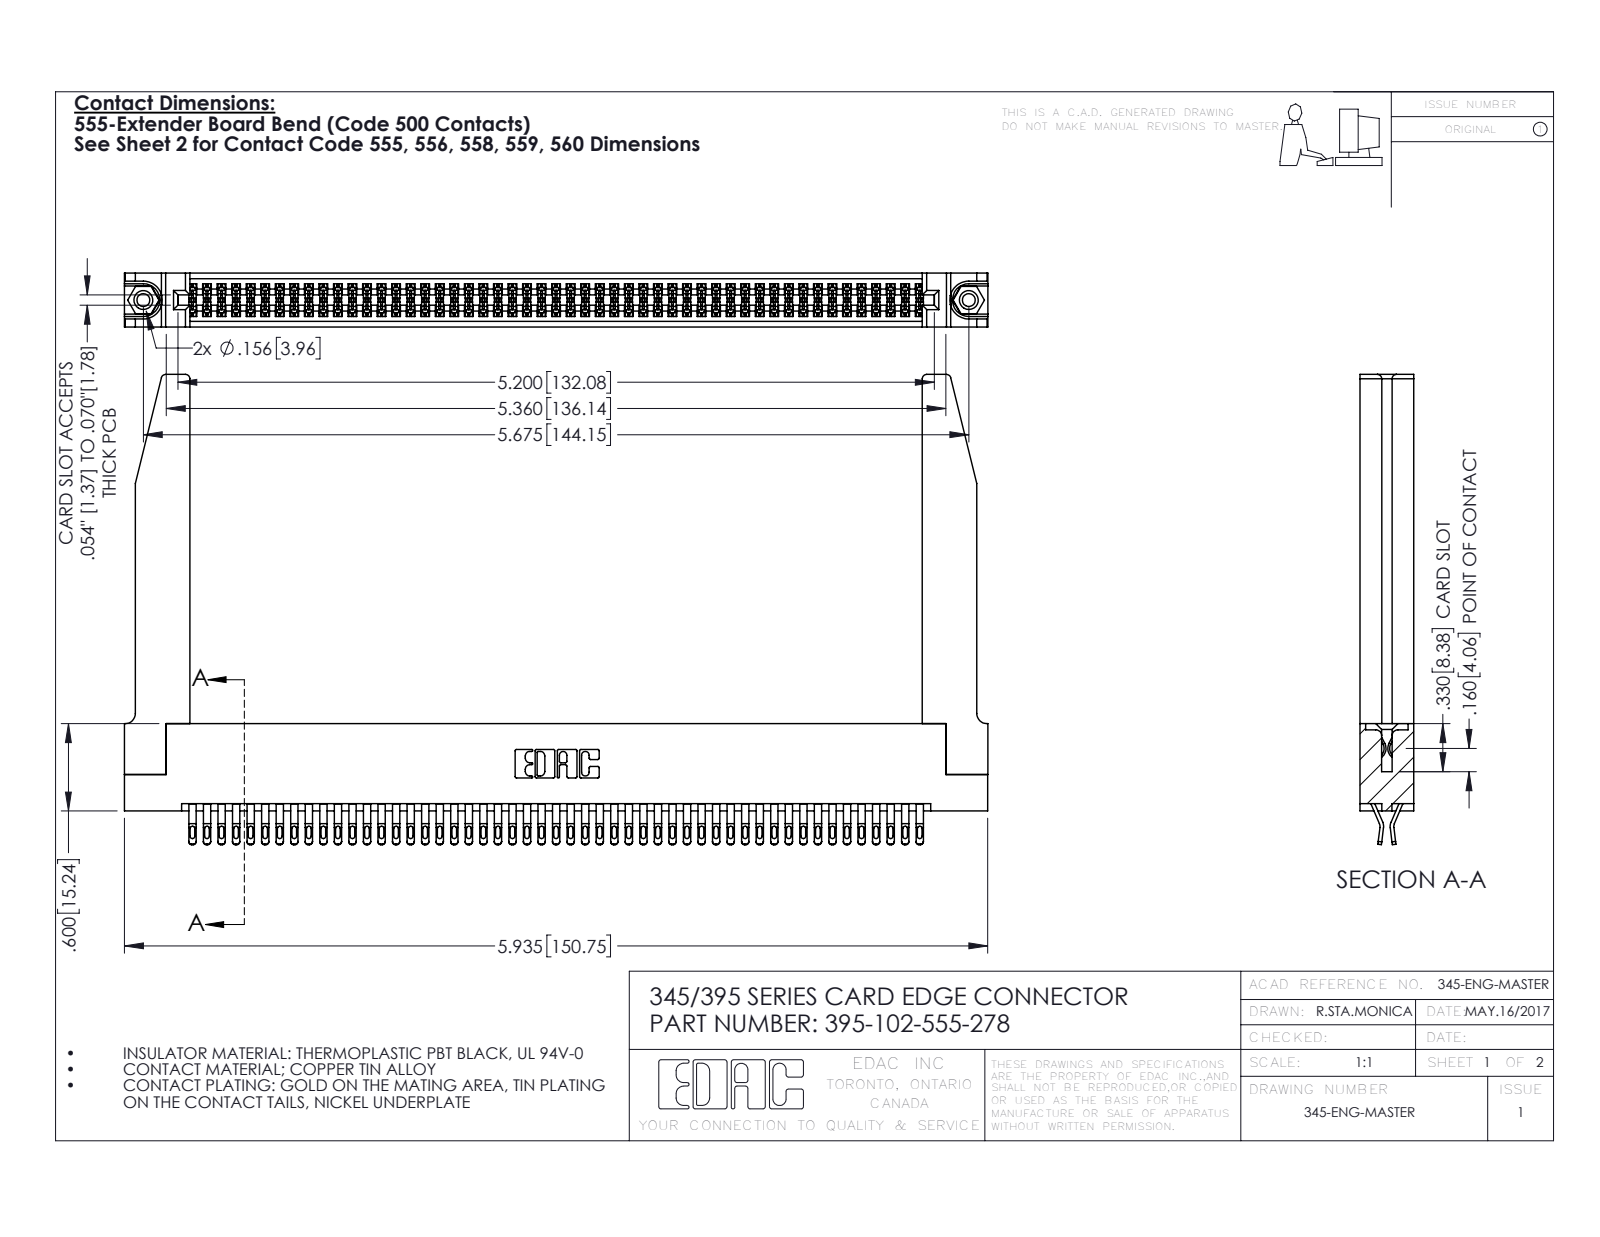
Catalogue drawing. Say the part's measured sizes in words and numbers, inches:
The part is named "345-292-001_555 Tail; 345-220-078_345-220-078; 345-250-001_345-250-001-102; 345 Part_Flush Mounting Lugs - 0.156 Dia-TH (+1 more)". Its 3-D file was written by "SolidWorks 2016 (CONFIG_CONTROL_DESIGN)". It is 107 solids with 6072 faces: 3384 planar, 2636 cylindrical and 52 other. Overall it measures 5.936 by 3.232 by 0.37 inches. Its volume is 1.391 cubic inches and its surface area 46.89 square inches. Round holes: 2 of diameter 0.089, 2 of diameter 0.125, 2 of diameter 0.156, 1 of diameter 0.064. Round bosses or shafts: 2 of diameter 0.155. Partial cylindrical surfaces (rounded edges, fillets, slot ends): 255 of radius 0.016, 204 of radius 0.02, 153 of radius 0.006, 22 of radius 0.01, 8 of radius 0.03, 6 of radius 0.007, 6 of radius 0.031, 3 of radius 0.026. The main face-to-face distances are 0.072, 0.37, 0.298, 0.025, 0.2, 0.098, 0.272, 0.225, 0.175, 0.148. The hole center spacings are 0.27, 5.439, 5.675.
